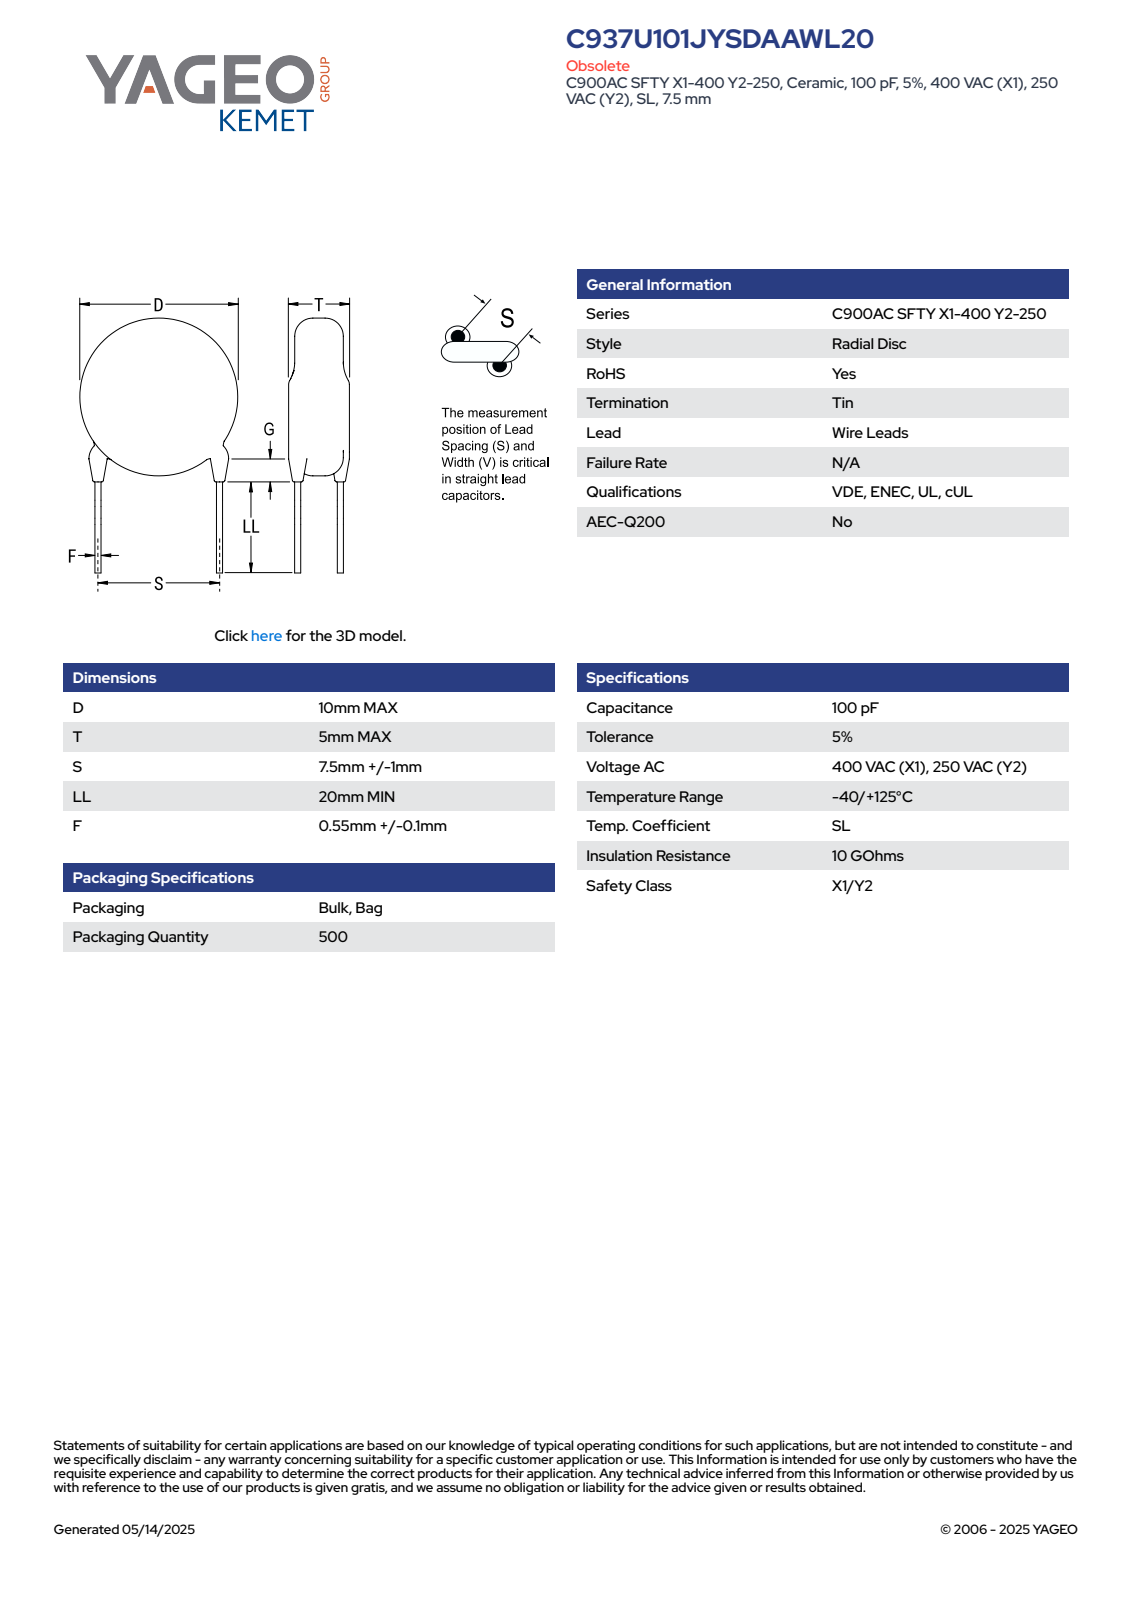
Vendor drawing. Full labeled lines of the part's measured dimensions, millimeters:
Part name (STEP PRODUCT): CCD_STC900_D10T5S7.5LL20F0.65G3
STEP written by: SolidWorks 2014 (AUTOMOTIVE_DESIGN)
Units: millimetres
Bodies: 4 solids, 83 faces (61 planar, 6 cylindrical, 16 other)
Overall size (bounding box): 30.28 × 10 × 5
Volume: 395 mm³ · Surface area: 383 mm²
Round bosses / shafts (diameter × count): ⌀0.65 ×2, ⌀10 ×1
Main face-to-face distances: 5, 25.85, 24.7, 1.15, 0.93, 0.42, 0.31, 3.43, 3.56, 1.89
